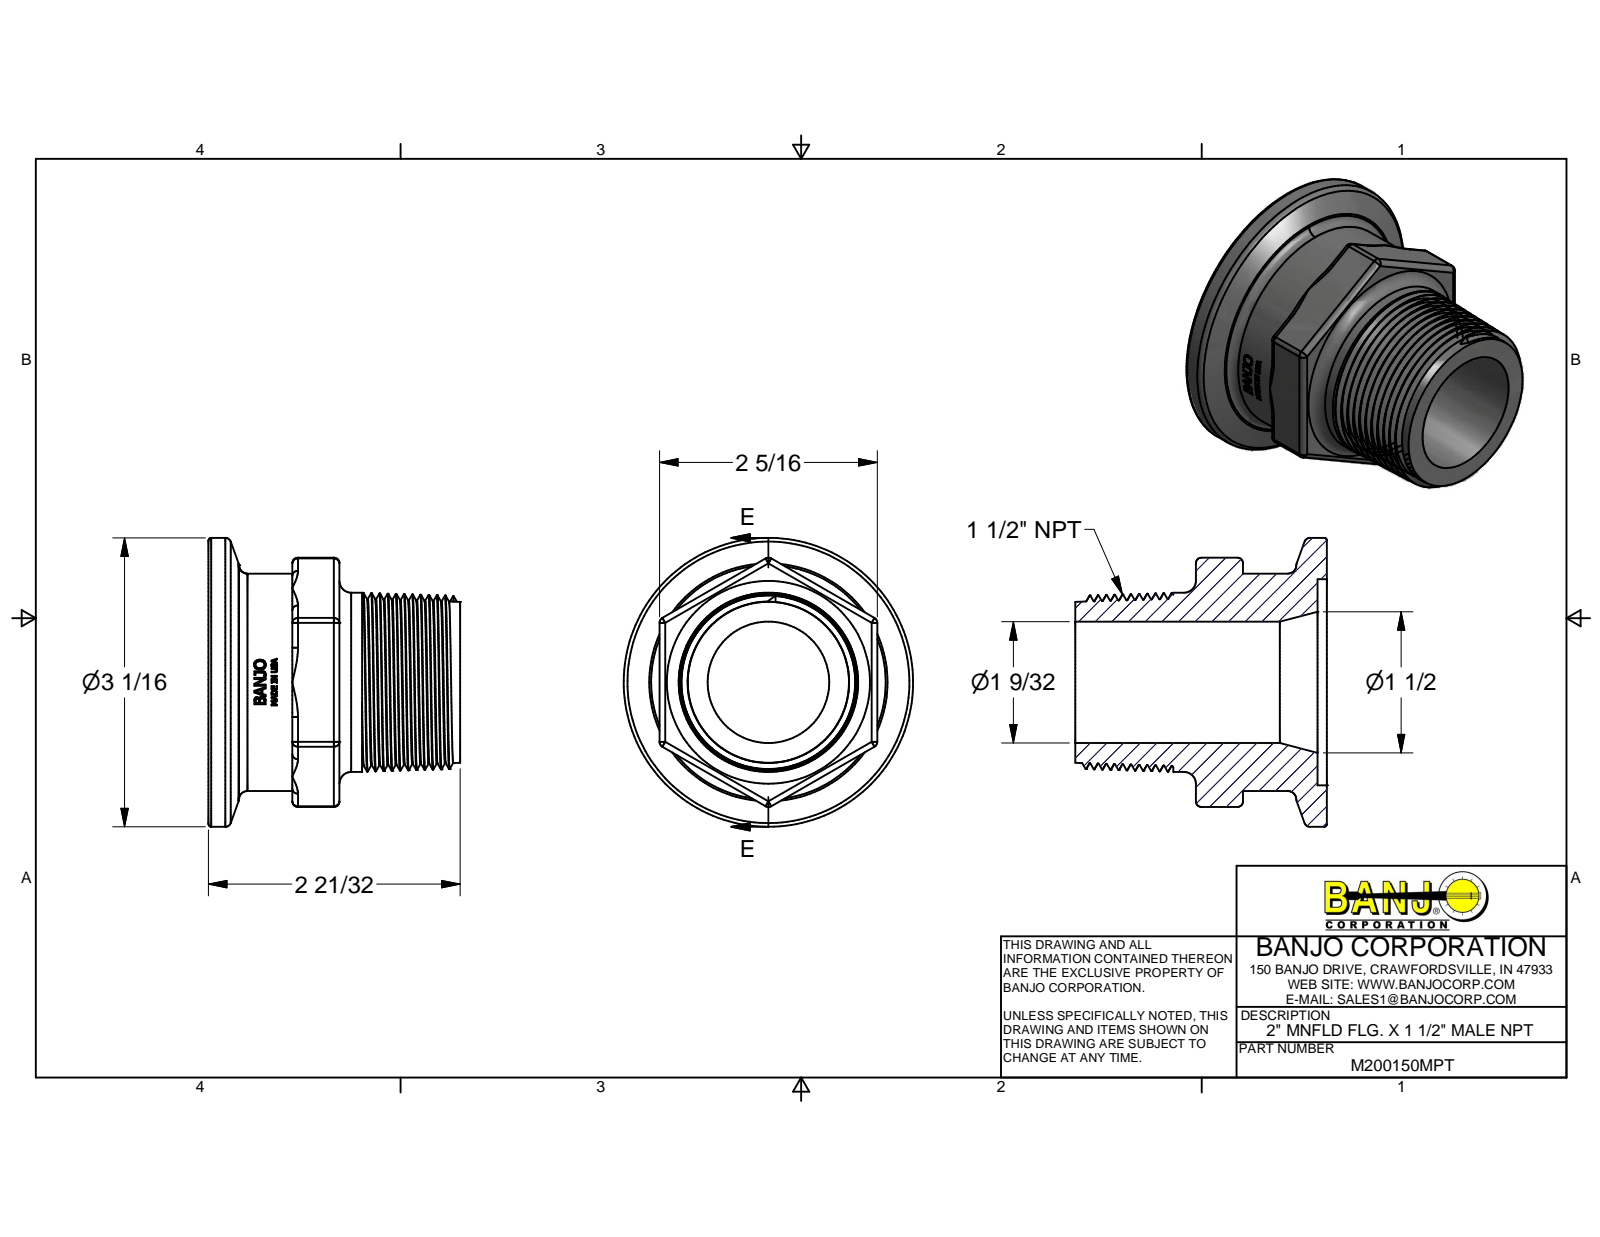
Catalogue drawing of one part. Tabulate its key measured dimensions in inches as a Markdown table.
| quantity | value |
| --- | --- |
| part name | M200150MPT |
| STEP written by | Autodesk Inventor 2013 (AUTOMOTIVE_DESIGN) |
| units | inches |
| bodies | 1 solid, 452 faces (206 planar, 64 cylindrical, 182 other) |
| overall size | 3.07 × 3.07 × 2.67 |
| volume | 6.474 in³ |
| surface area | 45.02 in² |
| round holes (diameter × count) | 1.29 × 1, 2.19 × 1 |
| round bosses / shafts (diameter × count) | 3.07 × 1, 2.31 × 1, 1.905 × 1 |
| partial cylindrical surfaces (radius × count) | 0.06 × 18, 1.125 × 1 |
| main face-to-face distances | 0.1, 2.31, 2.57, 2.67, 1.28, 1.29, 1.39, 1.04, 0.24, 1.53 |
